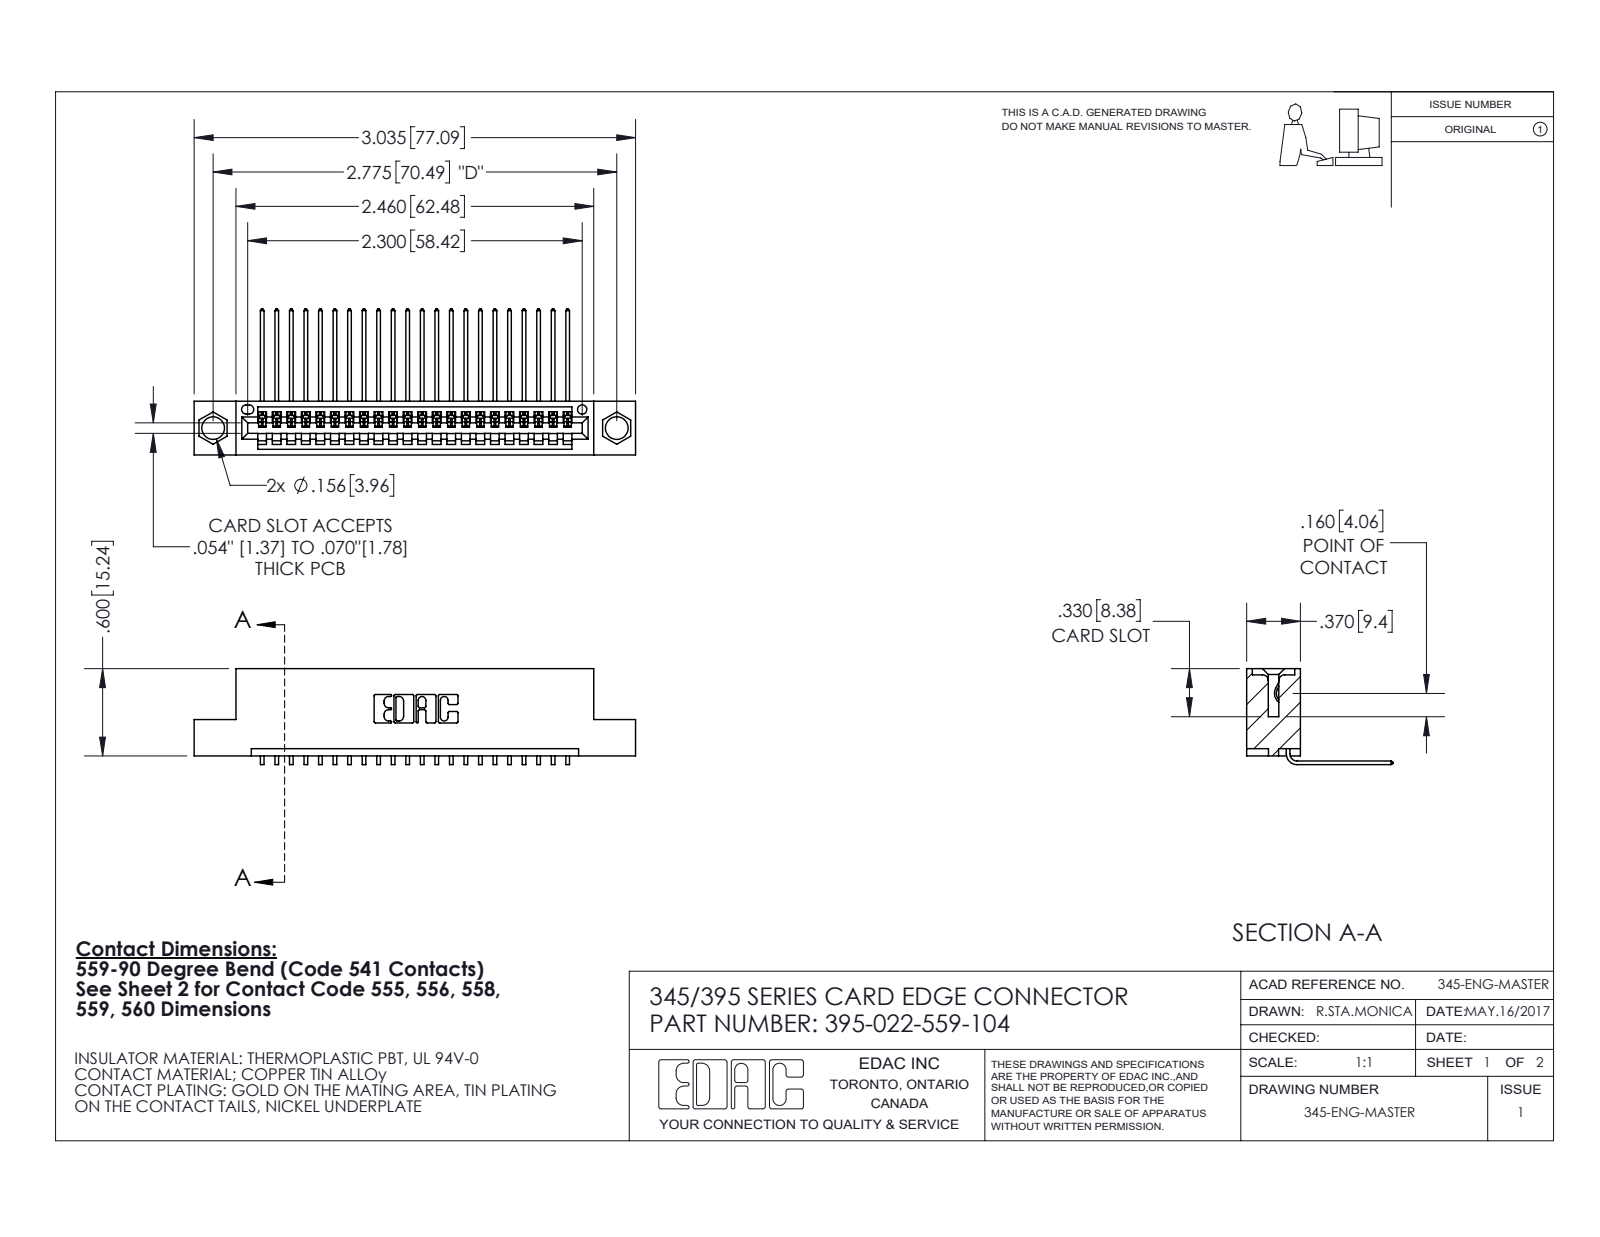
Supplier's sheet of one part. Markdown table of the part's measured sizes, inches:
| quantity | value |
| --- | --- |
| part name | 345-292-001_558 559 Tail - 1; 345 Part_Flush Mounting Lugs - 0.156 Dia-TI; 395-022-559-104 |
| STEP written by | SolidWorks 2020 (CONFIG_CONTROL_DESIGN) |
| units | inches |
| bodies | 23 solids, 1460 faces (1018 planar, 442 cylindrical, 0 other) |
| overall size | 3.035 × 1.005 × 0.659 |
| volume | 0.435 in³ |
| surface area | 14.68 in² |
| round holes (diameter × count) | 0.156 × 2, 0.064 × 1 |
| partial cylindrical surfaces (radius × count) | 0.006 × 44, 0.01 × 22, 0.007 × 6, 0.031 × 6, 0.026 × 3, 0.031 × 2, 0.04 × 2, 0.014 × 1 |
| main face-to-face distances | 0.072, 0.298, 0.37, 0.2, 0.098, 0.272, 0.025, 0.225, 0.149, 0.072 |
| hole center spacings | 0.27, 2.541, 2.775 |
